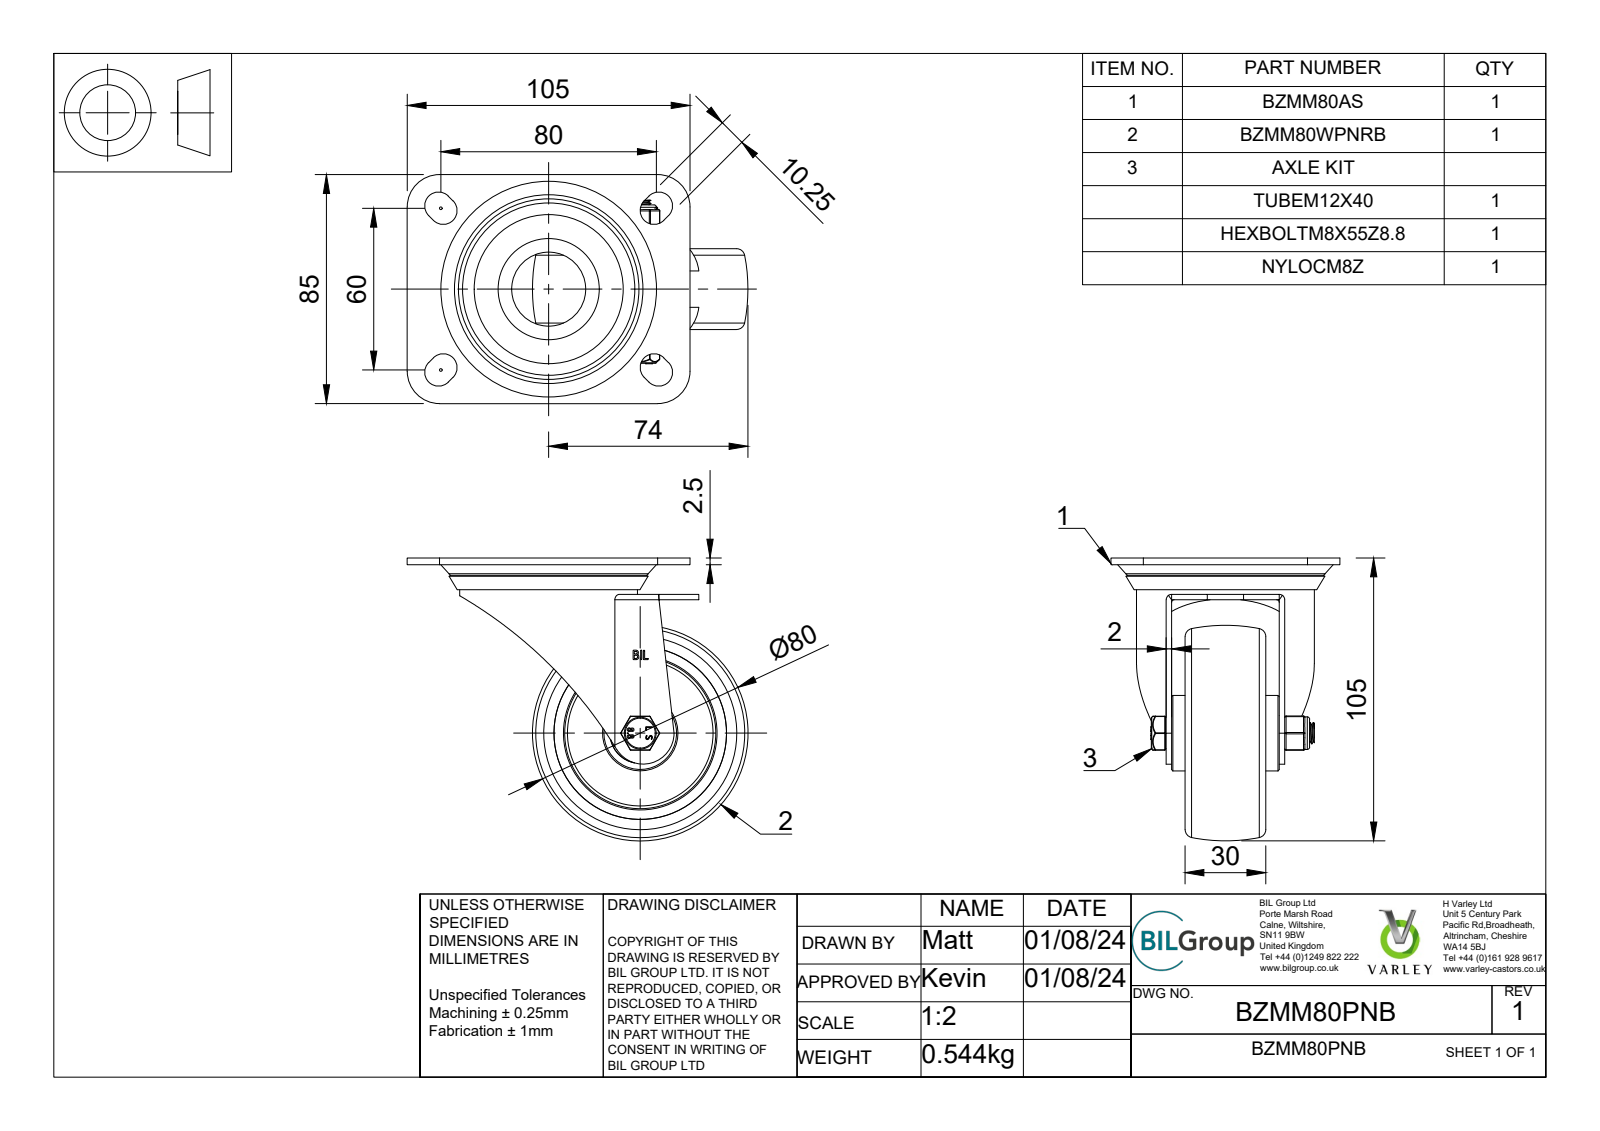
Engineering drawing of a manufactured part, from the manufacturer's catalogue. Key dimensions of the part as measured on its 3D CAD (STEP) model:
Part name (STEP PRODUCT): BZMM80PNB v4; BZMM80AS - 2 v1; ZINC PLATED, PRESSED STEEL TOP PLATE 1; ZINC PLATED, PRESSED STEEL TOP PLATE 1 Geometry (+7 more)
STEP written by: Autodesk Translation Framework v13.14.0.145 (AUTOMOTIVE_DESIGN)
Units: millimetres
Bodies: 41 solids, 457 faces (175 planar, 163 cylindrical, 119 other)
Overall size (bounding box): 126.5 × 105 × 85
Volume: 155 510 mm³ · Surface area: 99 117 mm²
Round holes (diameter × count): ⌀0.66 ×2, ⌀8 ×1, ⌀8.2 ×1, ⌀8.4 ×1, ⌀8.6 ×1, ⌀12.5 ×1, ⌀13 ×1, ⌀20 ×1, ⌀27.5 ×1, ⌀48 ×1, ⌀62 ×1, ⌀64 ×1
Round bosses / shafts (diameter × count): ⌀5.5 ×6, ⌀66 ×1, ⌀31.5 ×1, ⌀28 ×1, ⌀22.5 ×1, ⌀12.1 ×1, ⌀11.9 ×1, ⌀11.5 ×1
Partial cylindrical surfaces — rounded edges, fillets, slot ends (radius × count): R0.5 ×18, R0.25 ×12, R5.12 ×8, R0.33 ×4, R0.64 ×4, R1 ×4, R12 ×4, R0.63 ×2
Main face-to-face distances: 2, 5, 2.5, 13, 35, 17, 18, 7, 22, 37
Hole centre spacings: 3.22, 2.49
